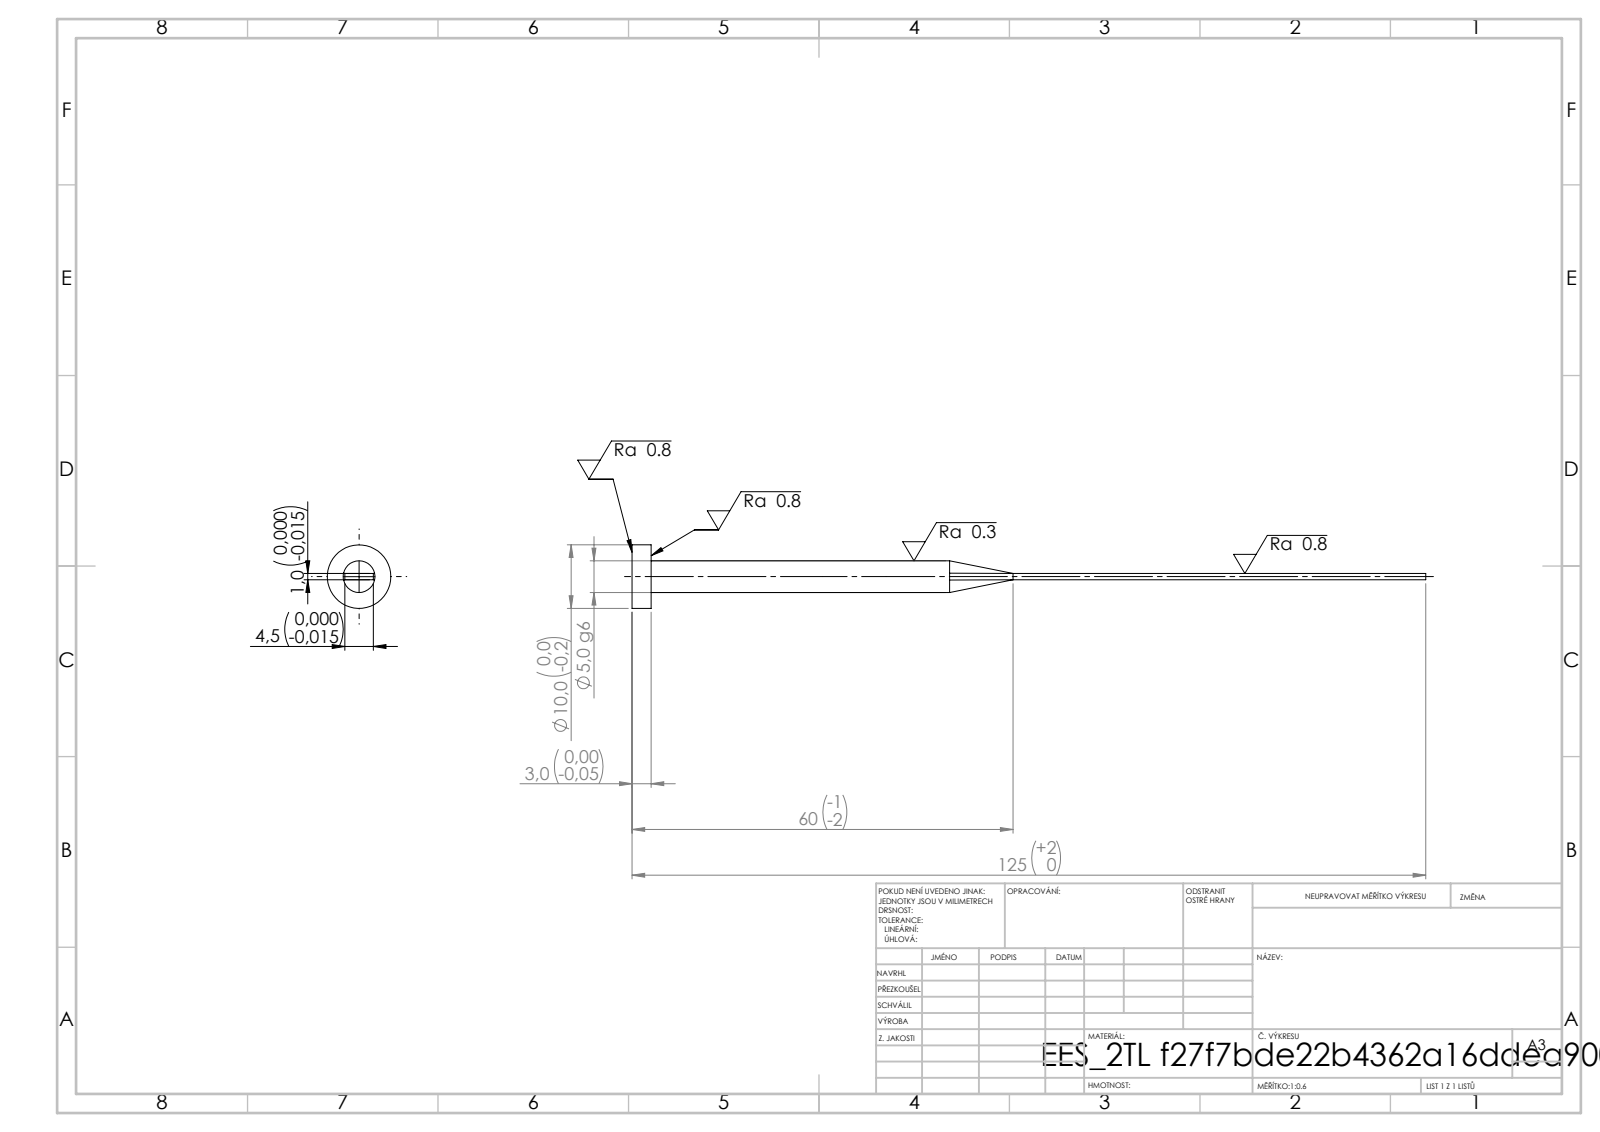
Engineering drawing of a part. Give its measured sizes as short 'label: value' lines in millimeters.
written by: SolidWorks 2019 (CONFIG_CONTROL_DESIGN)
unit: mm
bodies: 1 solid, 15 faces (7 planar, 4 cylindrical, 4 other)
size: 125 × 10 × 10
volume: 1 565 mm³; area: 1 818 mm²
bosses: 1× ⌀10, 1× ⌀5
face distances: 1, 4.5, 3, 125, 122
